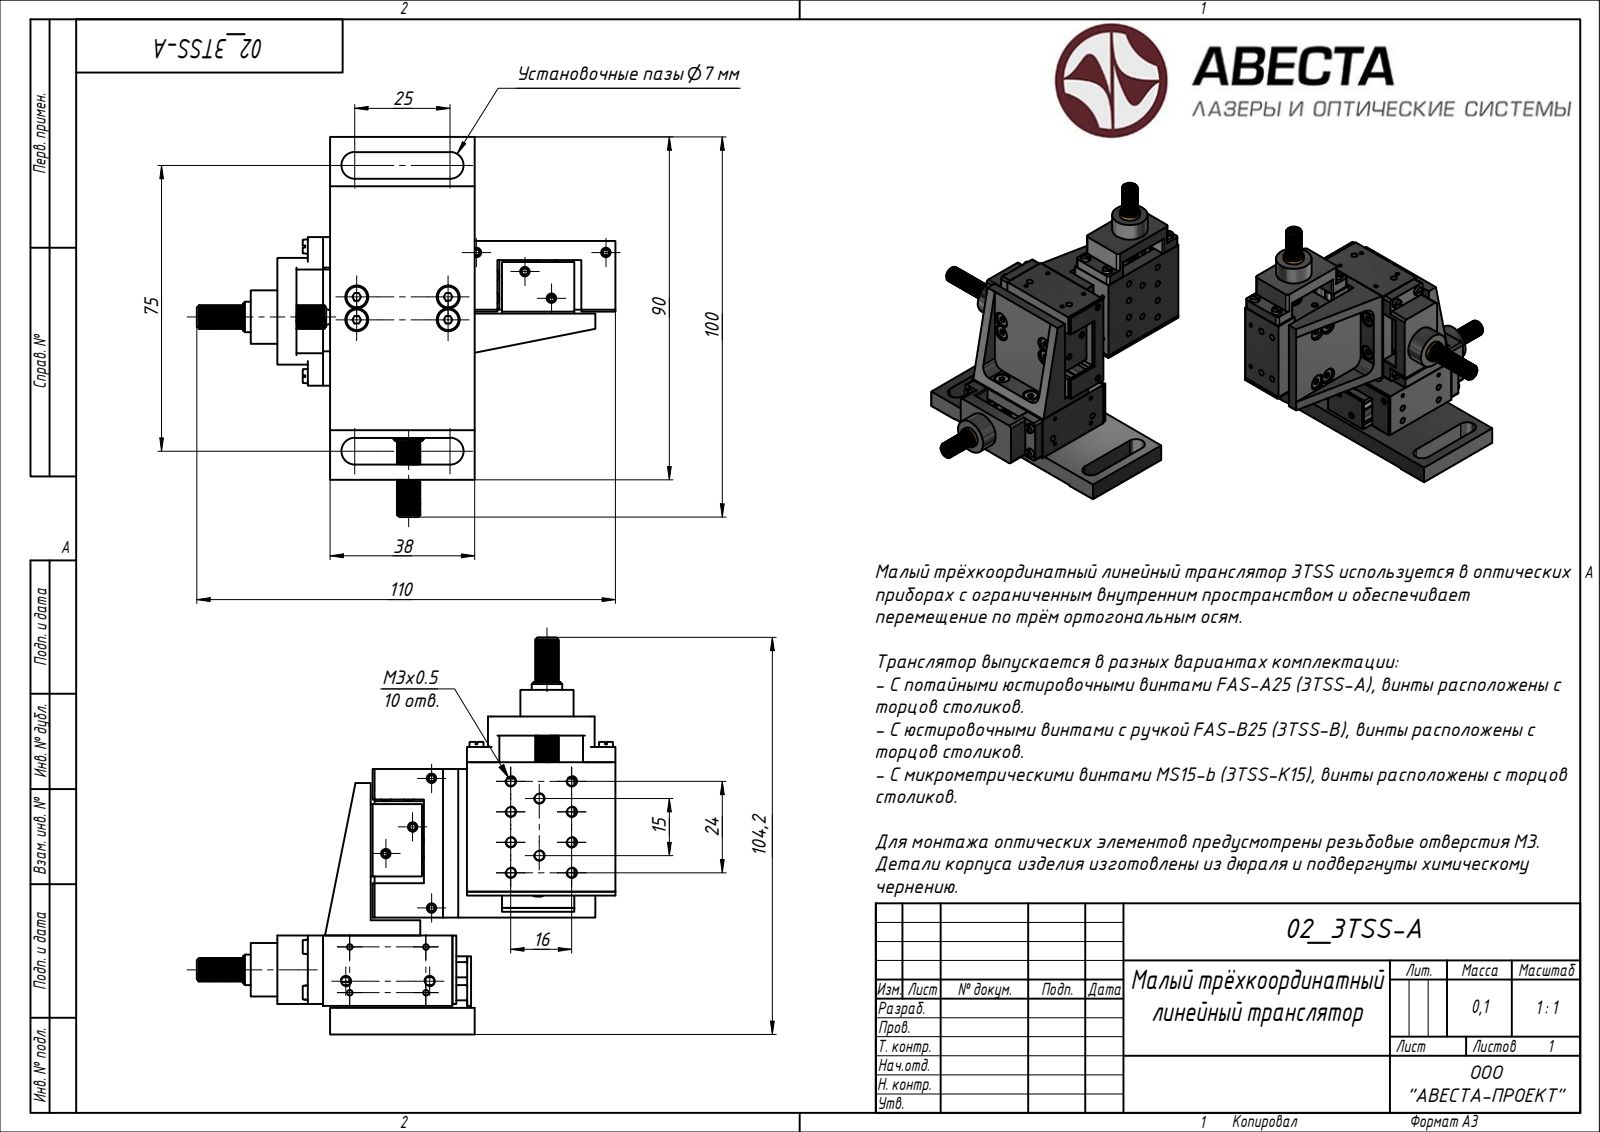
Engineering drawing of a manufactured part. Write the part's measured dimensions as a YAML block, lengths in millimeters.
step_written_by: "Rhino 7.34 (AUTOMOTIVE_DESIGN)"
units: millimeters
bodies: {solids: 4, faces: 1928, planar: 586, cylindrical: 929, other: 413}
overall_size: [109.95, 104.21, 99.79]
volume: 116406
surface_area: 69047
round_holes:
  - {diameter: 2.46, count: 46}
  - {diameter: 1.57, count: 19}
  - {diameter: 2.5, count: 18}
  - {diameter: 3.4, count: 16}
  - {diameter: 6, count: 15}
  - {diameter: 1.5, count: 12}
  - {diameter: 1.57, count: 8}
  - {diameter: 6.5, count: 8}
  - {diameter: 2.46, count: 7}
  - {diameter: 3.1, count: 3}
  - {diameter: 9.5, count: 3}
round_bosses_or_shafts:
  - {diameter: 4, count: 19}
  - {diameter: 5.54, count: 12}
  - {diameter: 3, count: 12}
  - {diameter: 5.35, count: 4}
  - {diameter: 14, count: 3}
  - {diameter: 9, count: 3}
  - {diameter: 8, count: 3}
  - {diameter: 6, count: 3}
partial_cylinders:
  - {radius: 1, count: 24}
  - {radius: 0.5, count: 12}
  - {radius: 2, count: 12}
  - {radius: 1.23, count: 7}
  - {radius: 1.23, count: 7}
  - {radius: 3.5, count: 4}
  - {radius: 4, count: 4}
  - {radius: 0.78, count: 3}
face_to_face_distances: [0.5, 1.5, 13.5, 2, 12, 11.5, 4.5, 5, 26.5, 39]
hole_center_spacings: [6, 16, 7, 8, 12, 3.16, 17.89, 21.21]
